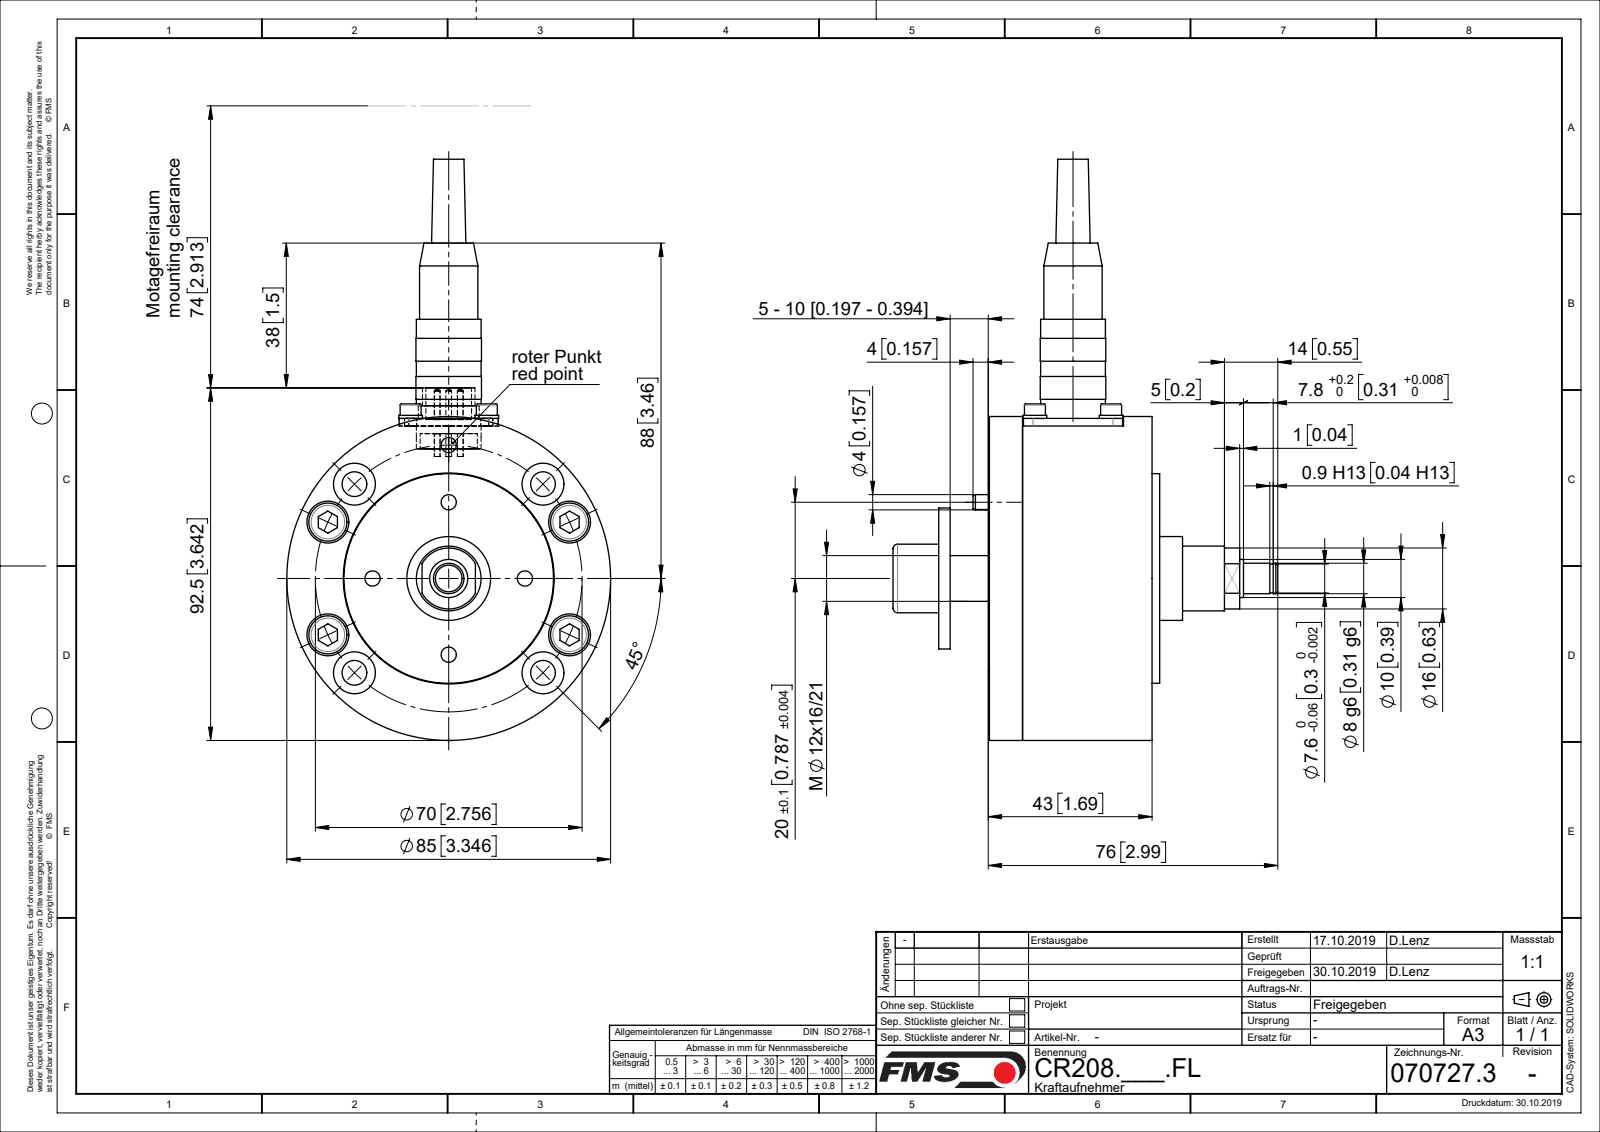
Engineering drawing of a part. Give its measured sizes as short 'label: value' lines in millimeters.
name: ZEICHNUNG2; C0707273; C0709081; C0612056 (+8 more)
written by: Mechanical Desktop 2009 (CONFIG_CONTROL_DESIGN)
unit: mm
bodies: 26 solids, 484 faces (149 planar, 249 cylindrical, 86 other)
size: 152.5 × 102 × 85
volume: 219 076 mm³; area: 84 142 mm²
holes: 8× ⌀6.5, 8× ⌀11, 4× ⌀2.6, 4× ⌀3.2, 4× ⌀4, 4× ⌀5.15, 4× ⌀7, 1× ⌀7.15, 1× ⌀10.68, 1× ⌀12, 1× ⌀13, 1× ⌀15
bosses: 5× ⌀10, 5× ⌀1.5, 4× ⌀6.2, 4× ⌀6, 4× ⌀5.5, 4× ⌀5, 4× ⌀3, 2× ⌀17
rounds: 4× R2.5, 2× R5, 1× R8
face distances: 6, 3, 9, 45, 10, 2, 34, 40, 43, 42
hole spacings: 20, 25.2, 35, 51.14, 28.28, 12.16, 14.14, 18.87
